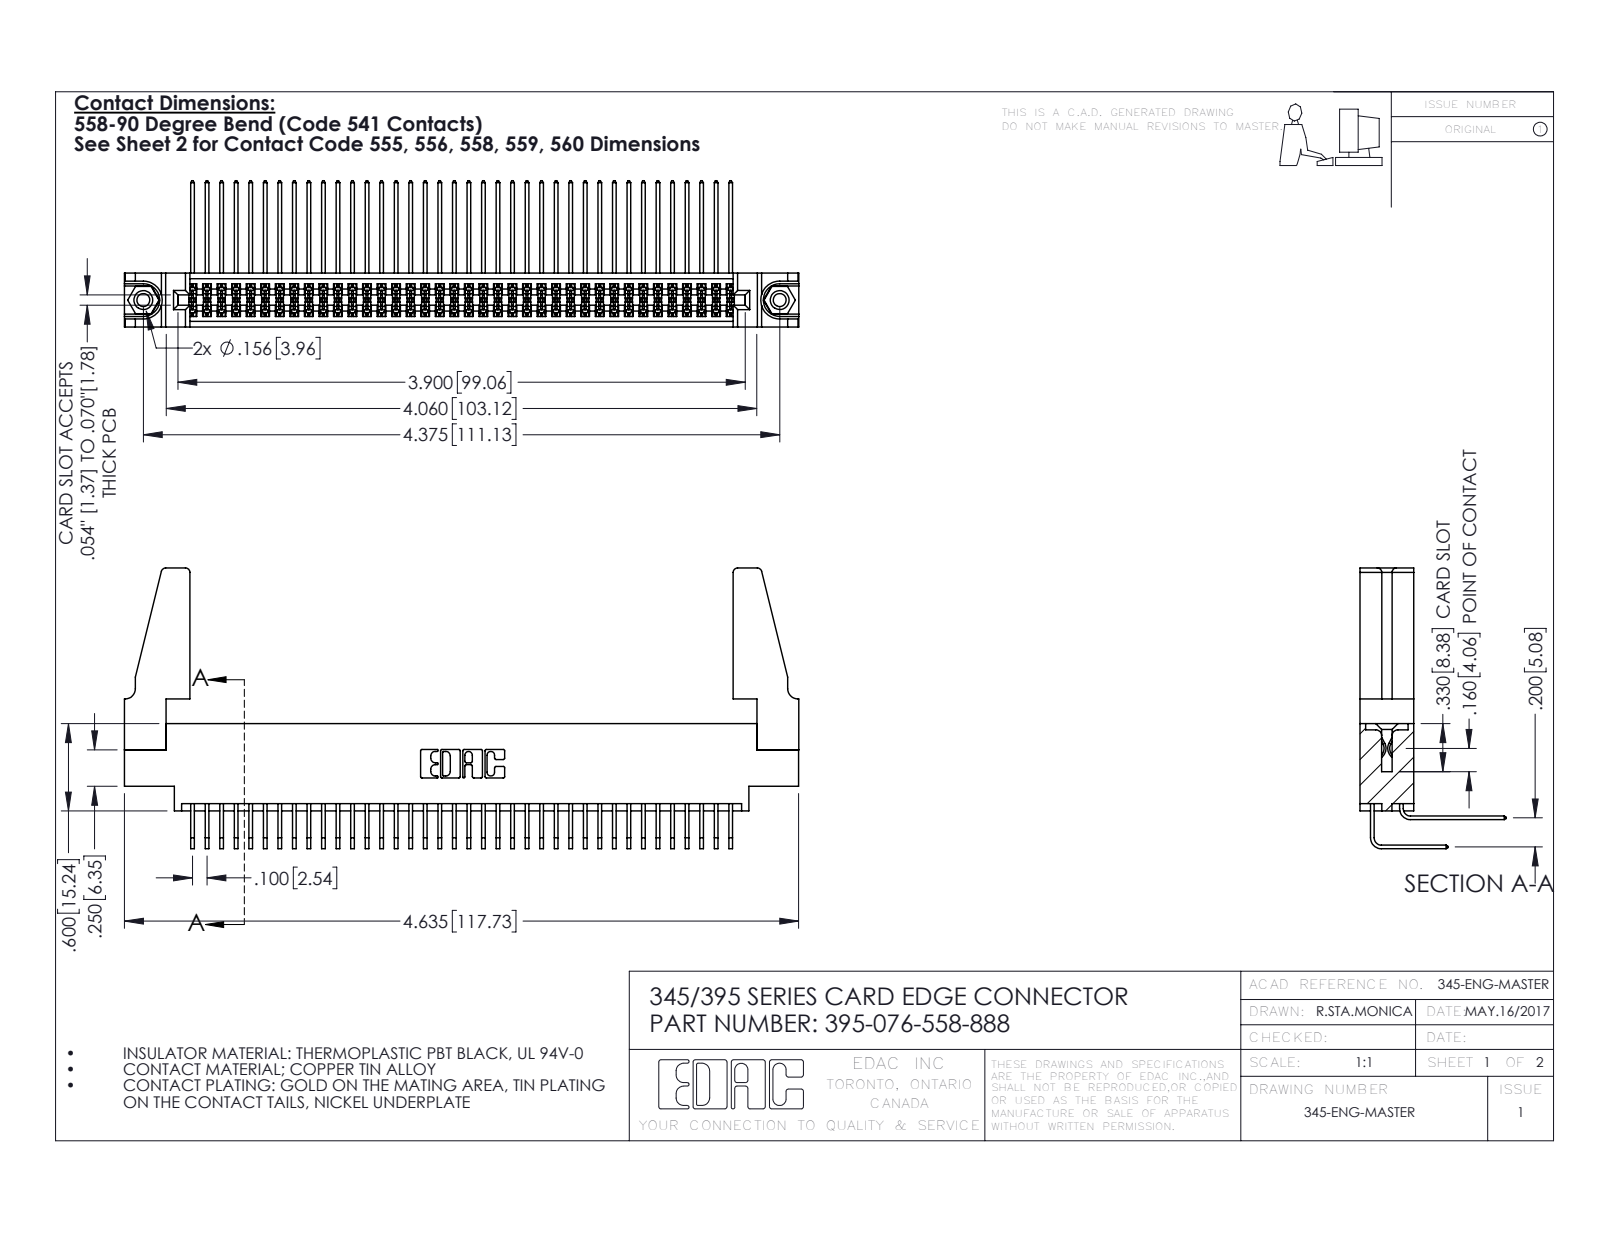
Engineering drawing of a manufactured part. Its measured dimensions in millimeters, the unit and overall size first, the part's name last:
Units: millimetres
Overall size (bounding box): 117.8 × 49 × 25.5
Round holes (diameter × count): ⌀2.3 ×2, ⌀3.2 ×2, ⌀4 ×2, ⌀1.6 ×1
Round bosses / shafts (diameter × count): ⌀3.9 ×2
Partial cylindrical surfaces — rounded edges, fillets, slot ends (radius × count): R0.2 ×114, R0.3 ×22, R0.8 ×8, R0.2 ×6, R0.8 ×6, R0.7 ×3, R0.4 ×2, R0.5 ×2
Main face-to-face distances: 1.8, 7.6, 9.4, 5.1, 2.5, 6.9, 0.6, 5.7, 4.4, 0.6
Hole centre spacings: 6.9, 105.1, 111.1
Volume: 15 000 mm³ · Surface area: 22 580 mm²
Bodies: 81 solids, 4206 faces (2816 planar, 1374 cylindrical, 16 other)
Part name (STEP PRODUCT): 345 Part_0.170 Offset - 0.156 Dia-TH; 345-292-001_558 559 Tail - 1; 345-292-001_558 Tail - 2; 345-220-078_345-220-088 (+2 more)
STEP written by: SolidWorks 2016 (CONFIG_CONTROL_DESIGN)
